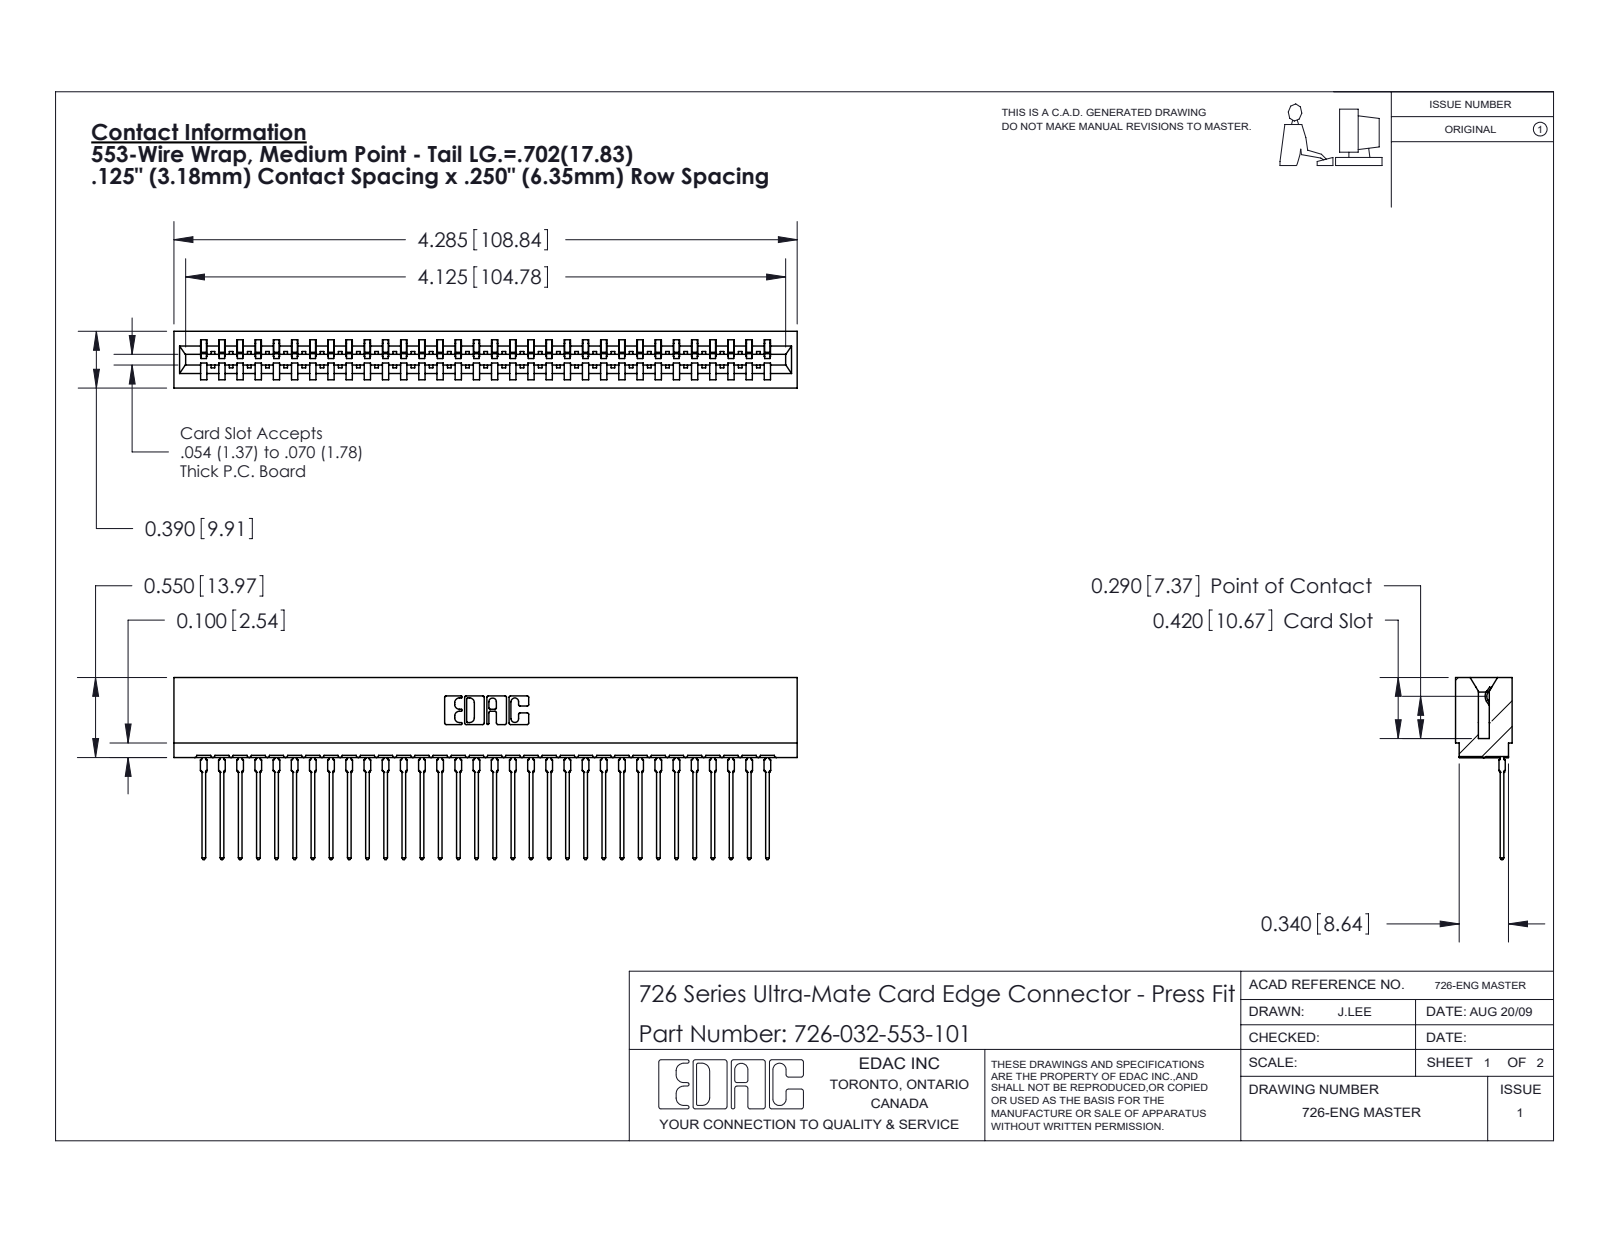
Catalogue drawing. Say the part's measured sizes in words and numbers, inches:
The part is named "746-292-001_553; 726 Part_.515 Slot Depth - 01; 726-032-553-101". Its 3-D file was written by "SolidWorks 2020 (CONFIG_CONTROL_DESIGN)". It is 33 solids with 3553 faces: 2071 planar, 650 cylindrical and 832 other. Overall it measures 4.285 by 1.251 by 0.39 inches. Its volume is 0.604 cubic inches and its surface area 24.1 square inches. Partial cylindrical surfaces (rounded edges, fillets, slot ends): 64 of radius 0.021, 33 of radius 0.015, 22 of radius 0.01, 6 of radius 0.007, 6 of radius 0.031, 4 of radius 0.005, 4 of radius 0.011, 3 of radius 0.026. The main face-to-face distances are 0.057, 0.333, 0.39, 0.25, 0.025, 0.307, 0.083, 0.275, 0.365, 0.032.
